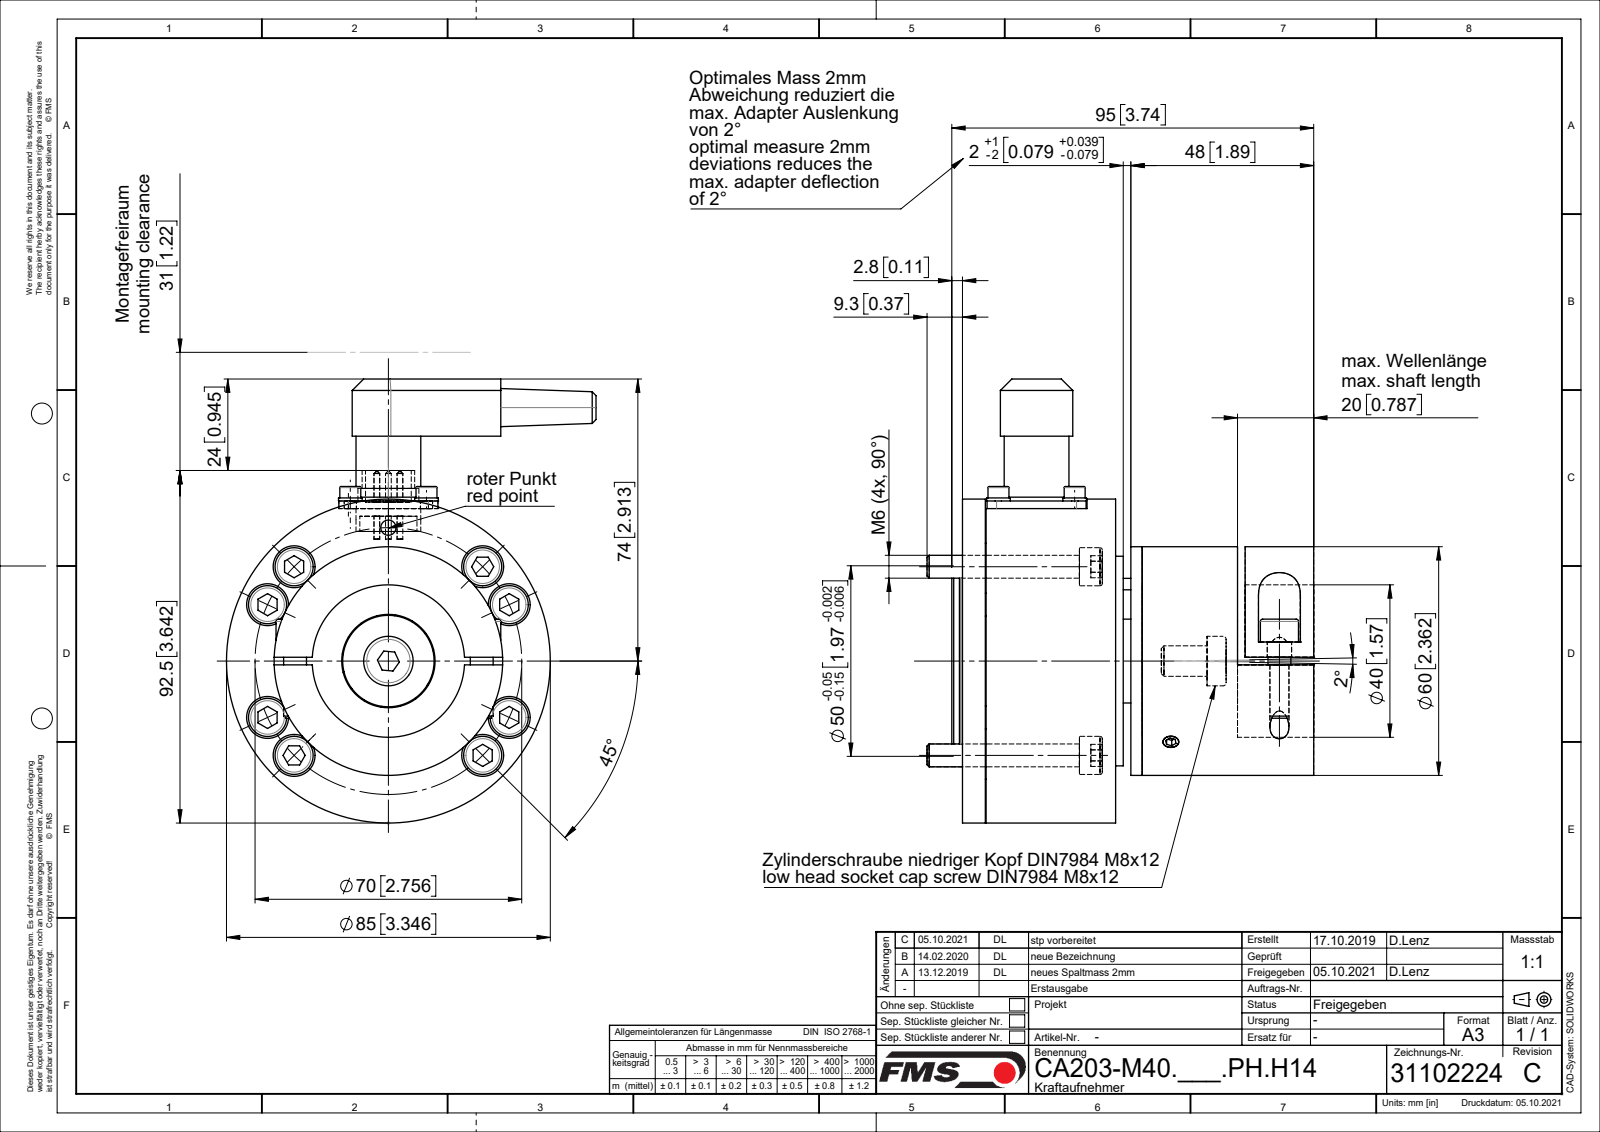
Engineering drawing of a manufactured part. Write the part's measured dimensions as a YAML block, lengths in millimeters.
part_name: "Flanschstecker_M14x1_Mini_5pol; RKL_6203_01; Se-Schr DIN7991_M3x8; 070907-2_01 (+8 more)"
step_written_by: "SolidWorks 2018 (CONFIG_CONTROL_DESIGN)"
units: millimeters
bodies: {solids: 44, faces: 839, planar: 302, cylindrical: 339, other: 198}
overall_size: [116.5, 101.5, 97]
volume: 291221
surface_area: 111461
round_holes:
  - {diameter: 2.5, count: 8}
  - {diameter: 6.5, count: 8}
  - {diameter: 11, count: 8}
  - {diameter: 5, count: 6}
  - {diameter: 2, count: 5}
  - {diameter: 4, count: 5}
  - {diameter: 3.1, count: 4}
  - {diameter: 3.2, count: 4}
  - {diameter: 3.6, count: 4}
  - {diameter: 7, count: 4}
  - {diameter: 6.4, count: 2}
  - {diameter: 3, count: 1}
round_bosses_or_shafts:
  - {diameter: 6, count: 11}
  - {diameter: 10, count: 10}
  - {diameter: 3, count: 8}
  - {diameter: 1.5, count: 5}
  - {diameter: 6.2, count: 4}
  - {diameter: 5.7, count: 4}
  - {diameter: 5.5, count: 4}
  - {diameter: 85, count: 1}
partial_cylinders:
  - {radius: 2.5, count: 4}
  - {radius: 5, count: 2}
  - {radius: 5.5, count: 2}
  - {radius: 9.5, count: 1}
face_to_face_distances: [2, 30, 41, 6, 10, 3, 45, 34, 15, 32]
hole_center_spacings: [35, 20, 24.78, 25.2, 32.8, 51.14, 56.46, 6]
